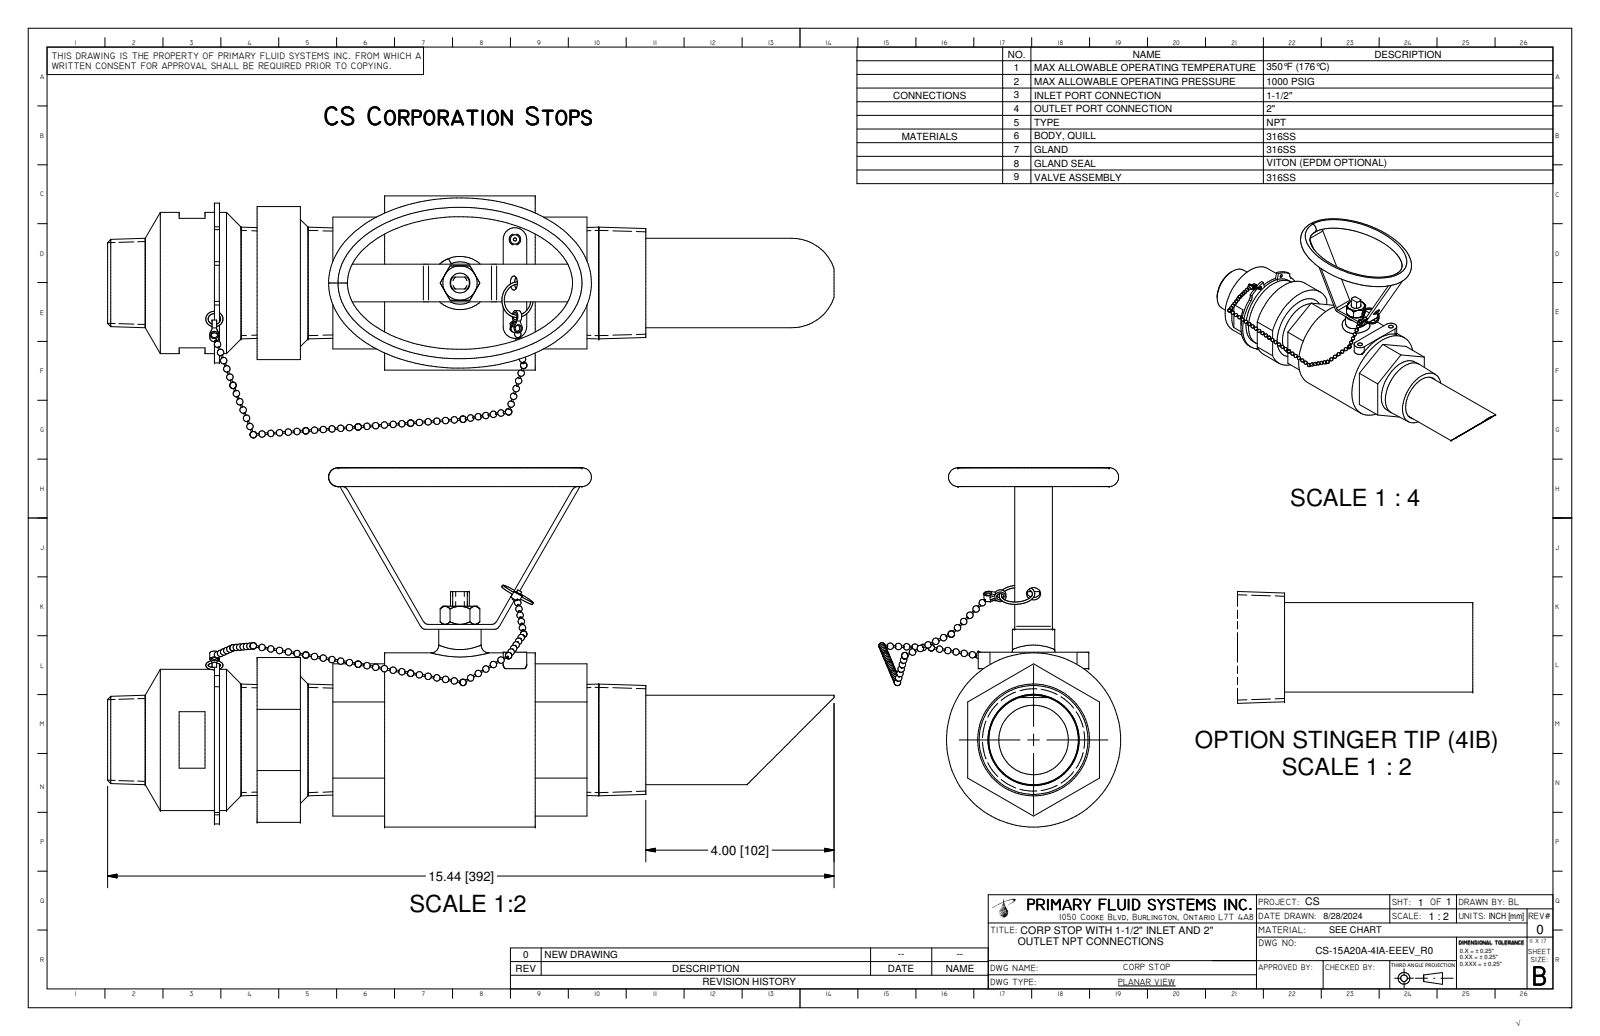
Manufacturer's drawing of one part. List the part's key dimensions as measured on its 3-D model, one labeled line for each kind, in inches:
STEP written by: Autodesk Inventor 2025 (CONFIG_CONTROL_DESIGN)
Units: inches
Bodies: 22 solids, 328 faces (124 planar, 110 cylindrical, 94 other)
Overall size (bounding box): 15.436 × 7.631 × 5.14
Volume: 66.63 in³ · Surface area: 415.5 in²
Round holes (diameter × count): ⌀0.067 ×2, ⌀0.118 ×2, ⌀0.15 ×2, ⌀0.157 ×2, ⌀0.2 ×2, ⌀0.3 ×1, ⌀0.42 ×1, ⌀1.476 ×1, ⌀1.5 ×1, ⌀1.93 ×1, ⌀1.939 ×1, ⌀2 ×1
Round bosses / shafts (diameter × count): ⌀0.035 ×9, ⌀0.236 ×2, ⌀3.7 ×1, ⌀3 ×1, ⌀2.72 ×1, ⌀2.333 ×1, ⌀1.9 ×1, ⌀0.9 ×1
Partial cylindrical surfaces — rounded edges, fillets, slot ends (radius × count): R0.125 ×8, R0.059 ×2, R0.098 ×2, R0.236 ×2, R0.25 ×2, R0.2 ×1, R1.698 ×1, R1.75 ×1
Main face-to-face distances: 2.8, 4.3, 1.1, 0.104, 7.011, 2.711, 5.911, 3.2, 0.225, 0.92
Hole centre spacings: 1.638, 0.314, 0.708, 1.24, 1.489, 1.489, 1.524, 1.85
